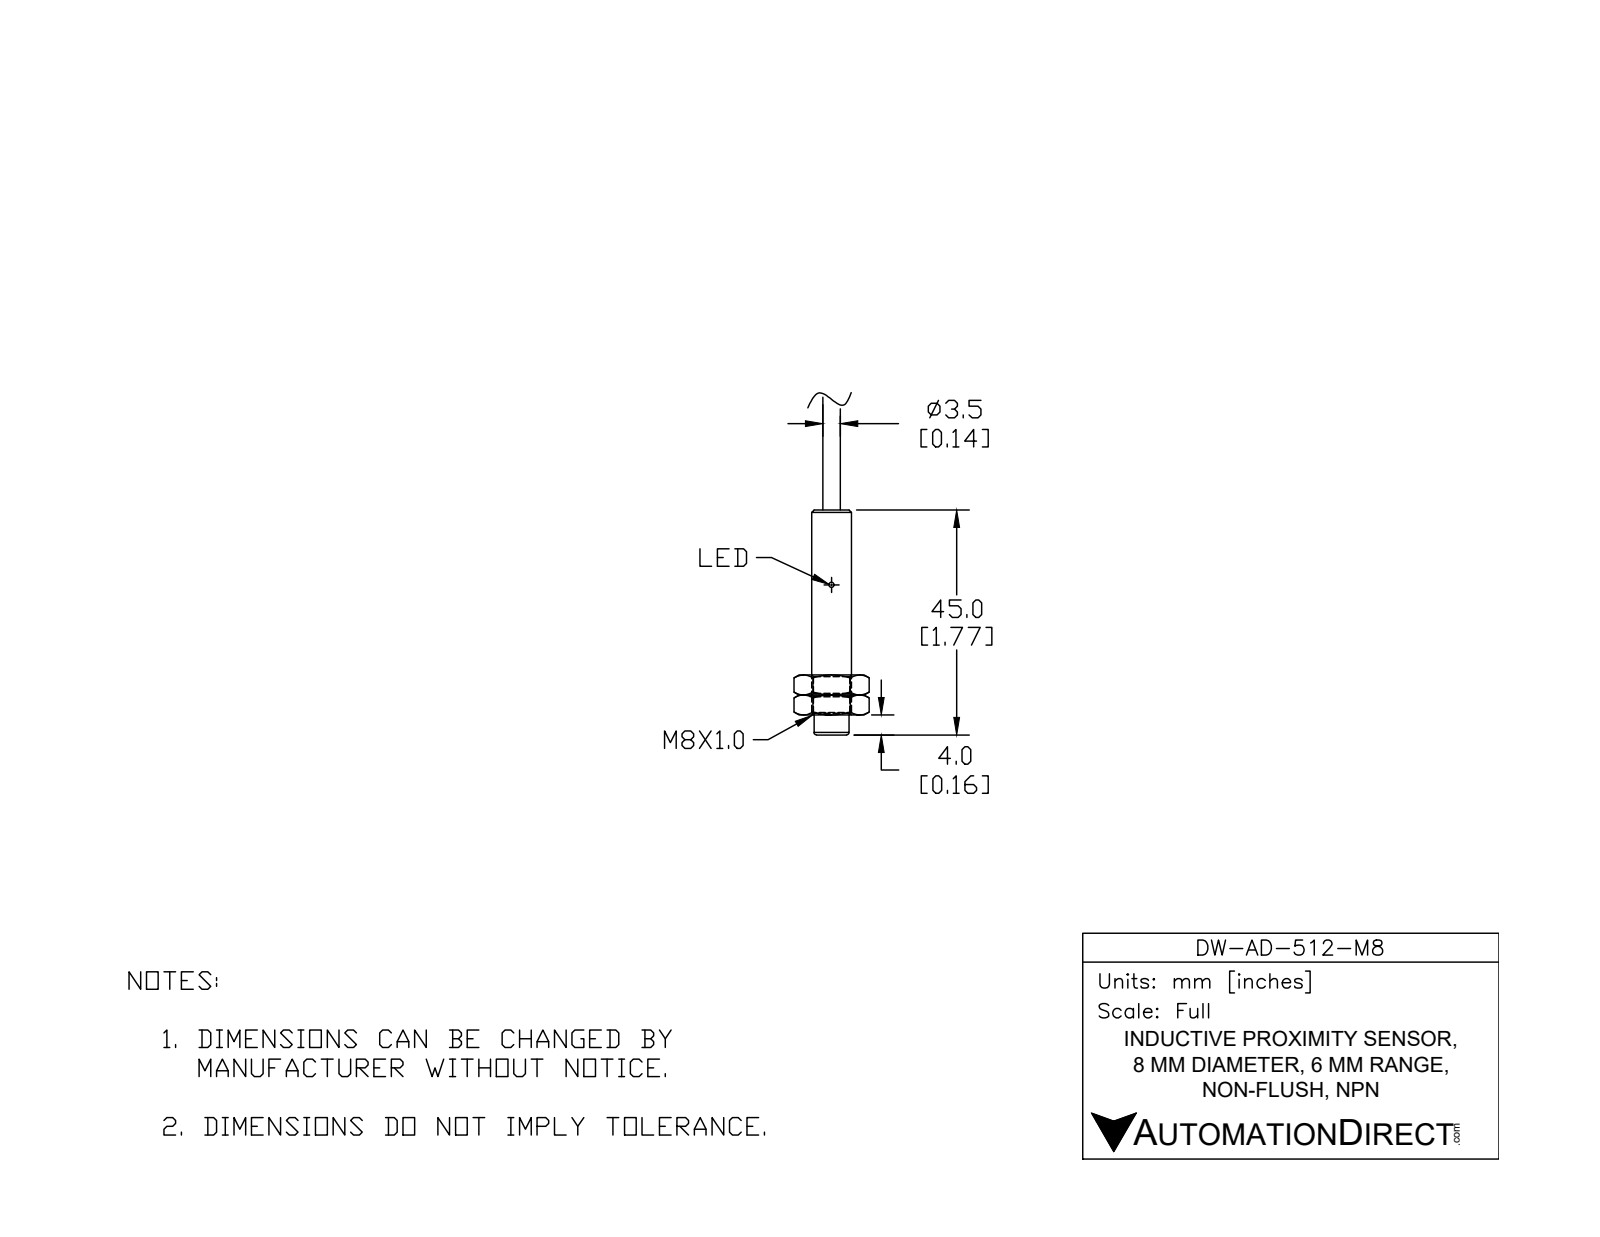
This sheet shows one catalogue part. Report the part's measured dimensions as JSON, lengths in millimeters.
{"part_name": "DW-AD-512-M8", "step_written_by": "SolidWorks 2017 (AUTOMOTIVE_DESIGN)", "units": "millimeters", "bodies": {"solids": 2, "faces": 14, "planar": 6, "cylindrical": 4, "other": 4}, "overall_size": [71.2, 8, 8], "volume_mm3": 2720, "surface_area_mm2": 1688, "round_bosses_or_shafts": [[8, 1], [6.9, 1], [6.5, 1], [5, 1]], "face_to_face_distances": [4.2, 71.2, 67, 45.5, 41.3, 25.7, 45, 40.8, 0.5, 26.2]}
